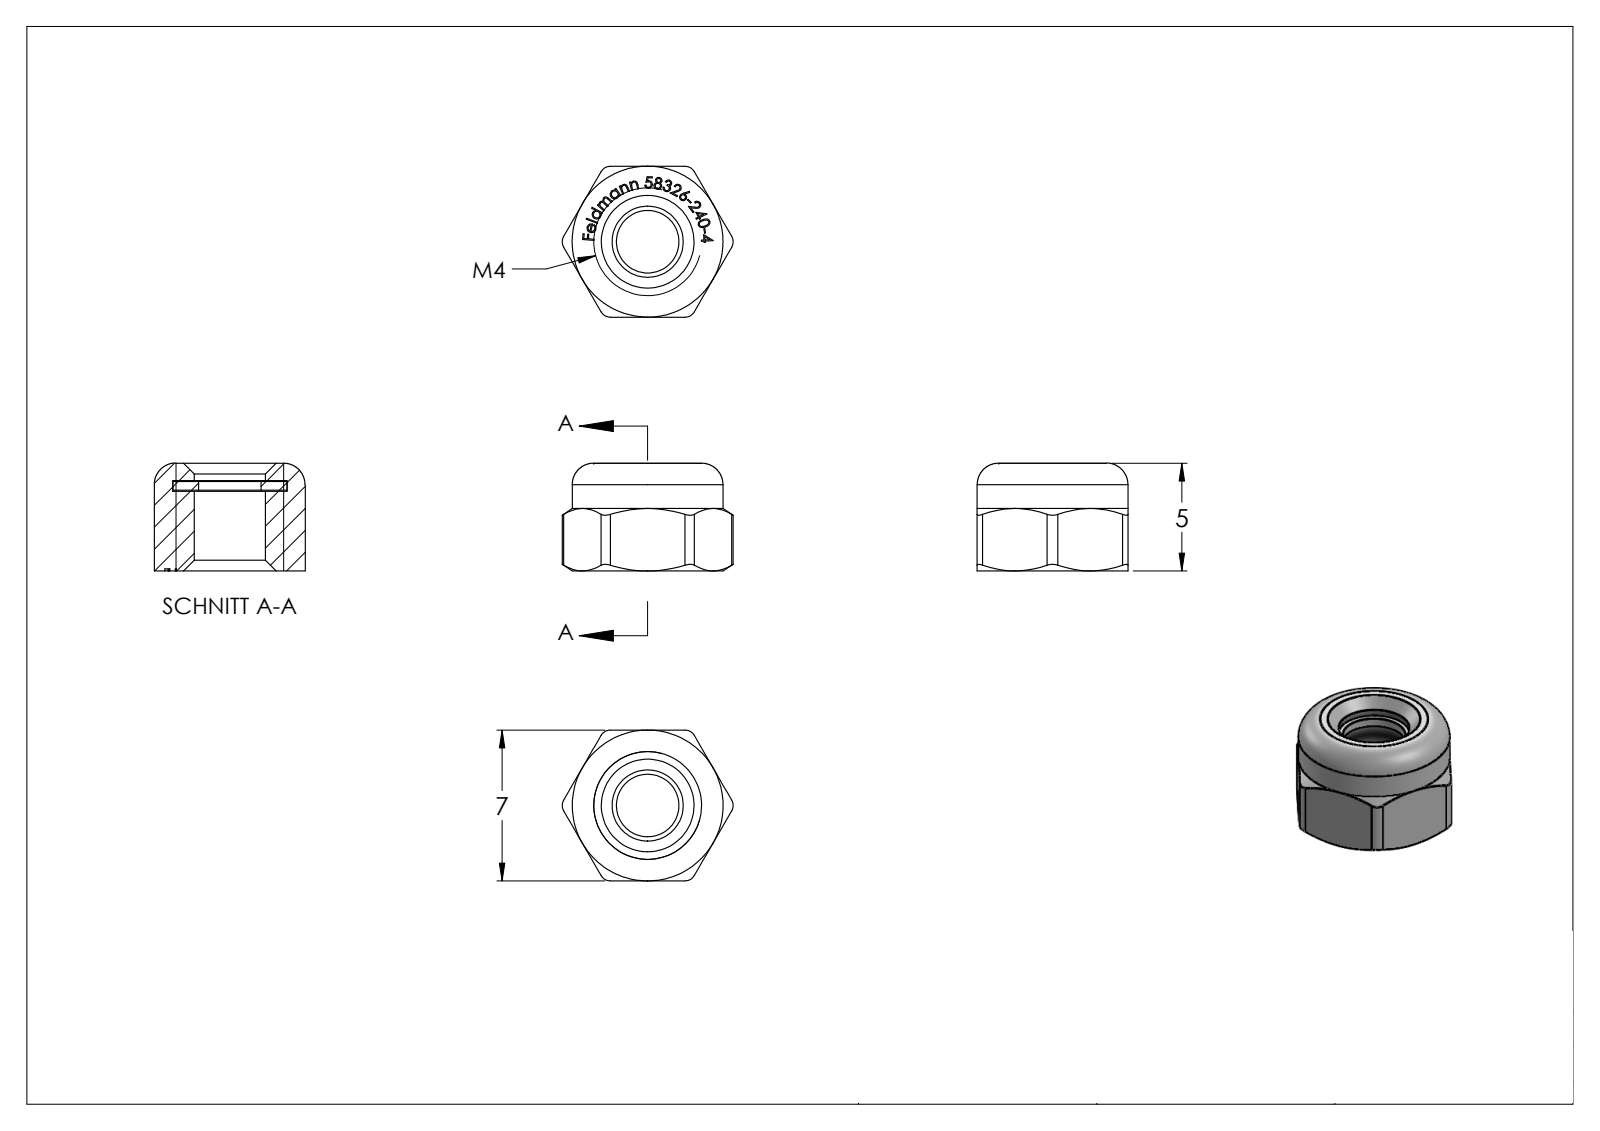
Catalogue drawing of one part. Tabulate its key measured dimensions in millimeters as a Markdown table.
| quantity | value |
| --- | --- |
| part name | 58326-240-4 |
| STEP written by | SolidWorks 2018 (CONFIG_CONTROL_DESIGN) |
| units | millimeters |
| bodies | 2 solids, 296 faces (152 planar, 12 cylindrical, 132 other) |
| overall size | 15 × 7.93 × 7 |
| volume | 152 mm³ |
| surface area | 291 mm² |
| round holes (diameter × count) | 2.9 × 1, 3.3 × 1, 5.3 × 1 |
| round bosses / shafts (diameter × count) | 7 × 1 |
| partial cylindrical surfaces (radius × count) | 0.5 × 6 |
| main face-to-face distances | 7, 0.45, 3.75, 4.15, 0.4, 3.7, 4.2, 0.5, 5, 1.3 |
